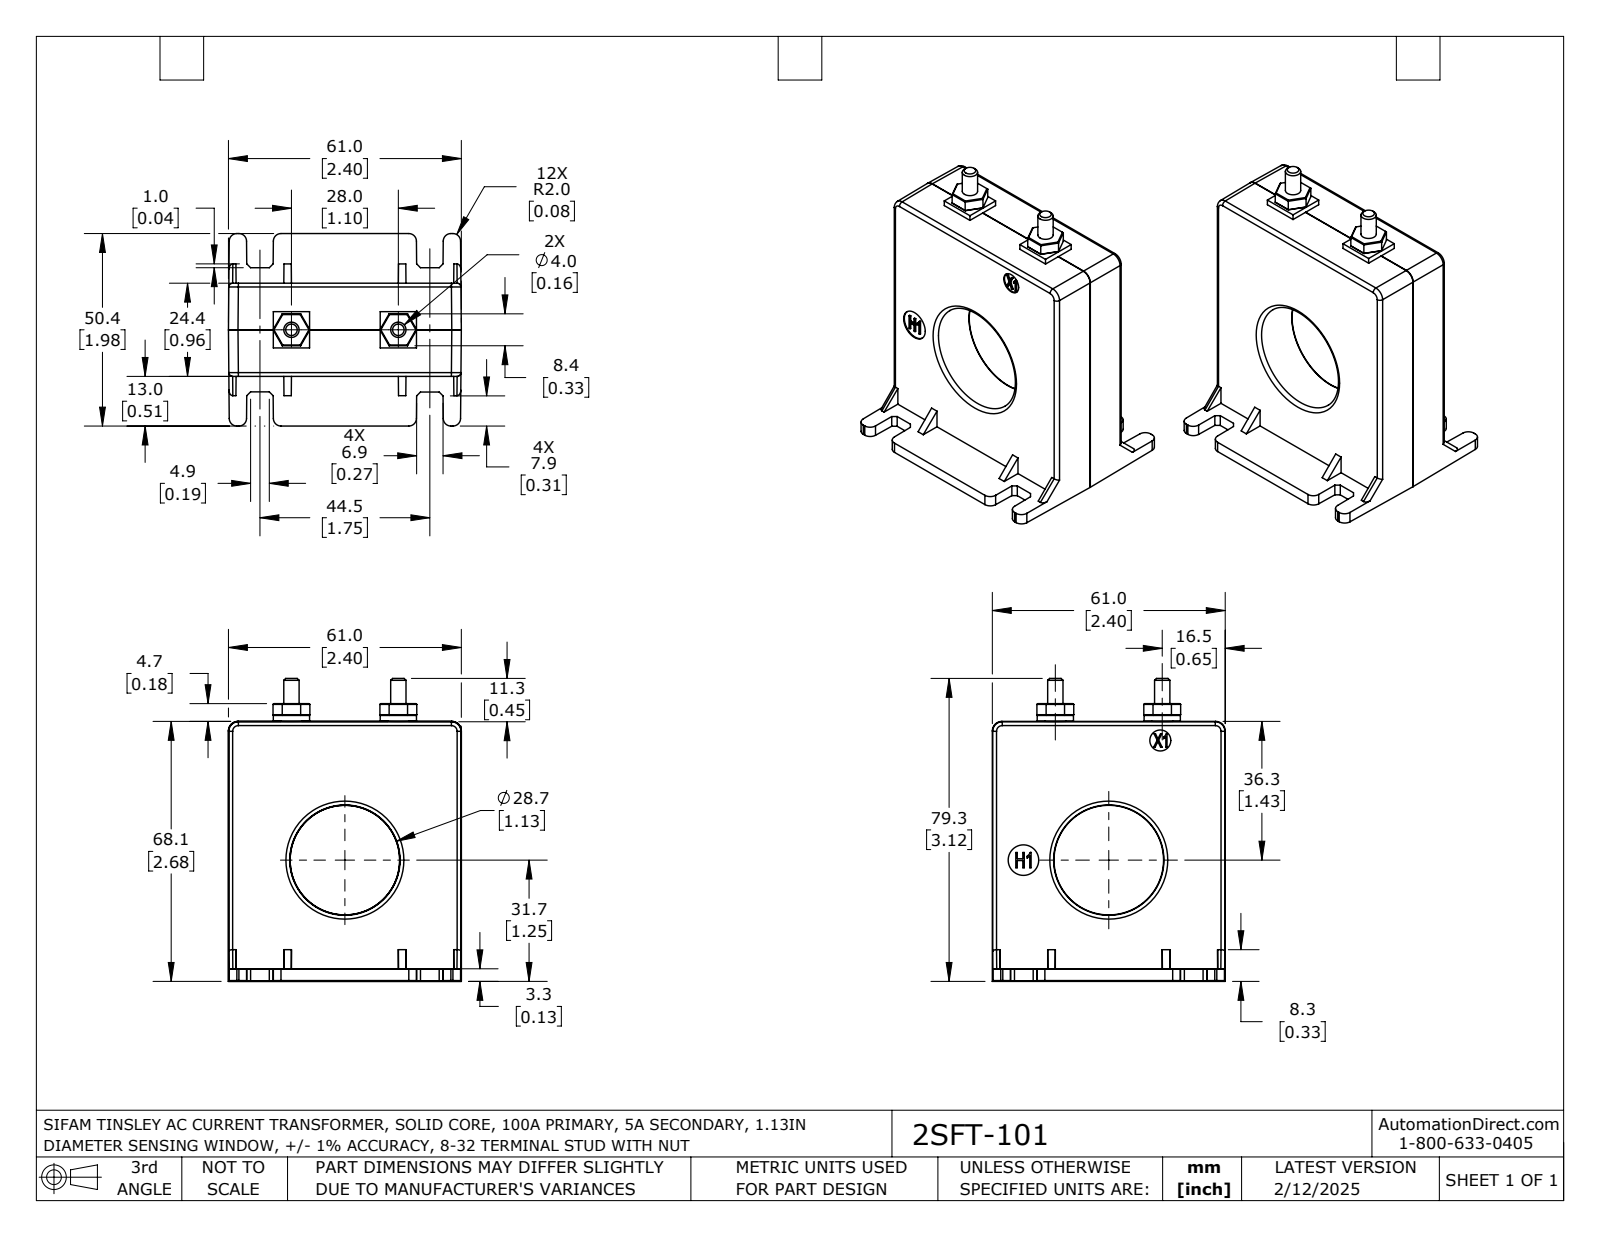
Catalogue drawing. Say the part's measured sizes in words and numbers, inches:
The part is named "2SFT-101". Its 3-D file was written by "SolidWorks 2021 (AUTOMOTIVE_DESIGN)". It is 1 solid with 245 faces: 183 planar, 38 cylindrical and 24 other. Overall it measures 3.123 by 2.402 by 1.984 inches. Its volume is 5.469 cubic inches and its surface area 40.07 square inches. Round holes: 1 of diameter 0.217, 1 of diameter 0.315. Round bosses or shafts: 2 of diameter 0.217, 2 of diameter 0.158. Partial cylindrical surfaces (rounded edges, fillets, slot ends): 12 of radius 0.079, 10 of radius 0.039, 4 of radius 0.098. The main face-to-face distances are 0.48, 0.476, 0.484, 0.961, 2.402, 0.134, 2.68, 2.546, 0.512, 0.992. The hole center spacings are 1.874.
